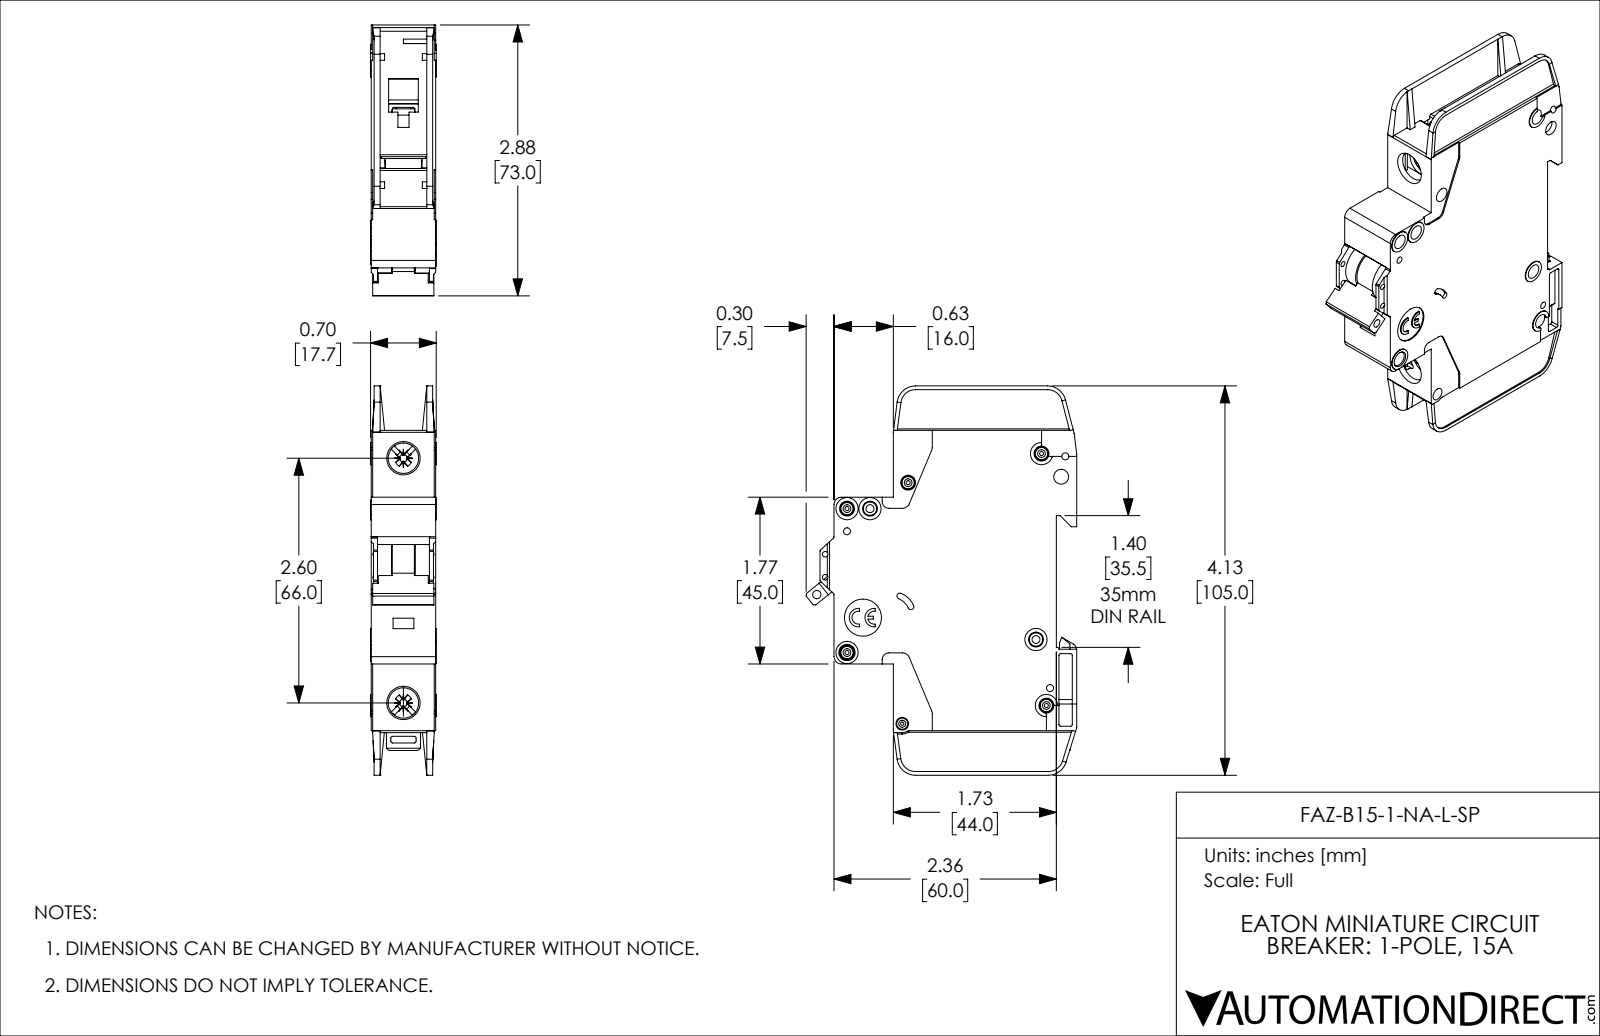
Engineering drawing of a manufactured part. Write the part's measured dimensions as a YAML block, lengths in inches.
part_name: "FAZ-B15-1-NA-L-SP"
step_written_by: "SolidWorks 2019 (AUTOMOTIVE_DESIGN)"
units: inches
bodies: {solids: 1, faces: 1127, planar: 671, cylindrical: 357, other: 99}
overall_size: [4.134, 2.876, 0.697]
volume: 4.682
surface_area: 41.01
round_holes:
  - {diameter: 0.157, count: 8}
  - {diameter: 0.043, count: 5}
  - {diameter: 0.075, count: 4}
  - {diameter: 0.059, count: 2}
  - {diameter: 0.085, count: 2}
  - {diameter: 0.323, count: 2}
  - {diameter: 0.035, count: 1}
  - {diameter: 0.089, count: 1}
  - {diameter: 0.098, count: 1}
  - {diameter: 0.134, count: 1}
  - {diameter: 0.394, count: 1}
round_bosses_or_shafts:
  - {diameter: 0.13, count: 5}
  - {diameter: 0.236, count: 4}
  - {diameter: 0.118, count: 2}
  - {diameter: 0.098, count: 1}
partial_cylinders:
  - {radius: 0.02, count: 42}
  - {radius: 0.016, count: 10}
  - {radius: 0.039, count: 10}
  - {radius: 0.079, count: 8}
  - {radius: 0.197, count: 5}
  - {radius: 0.008, count: 4}
  - {radius: 0.026, count: 4}
  - {radius: 0.043, count: 4}
face_to_face_distances: [0.047, 0.685, 0.591, 0.638, 0.094, 0.543, 0.016, 0.031, 0.496, 0.575]
hole_center_spacings: [0.244, 0.537, 0.87, 0.189, 0.199, 0.204, 0.221, 0.24]
